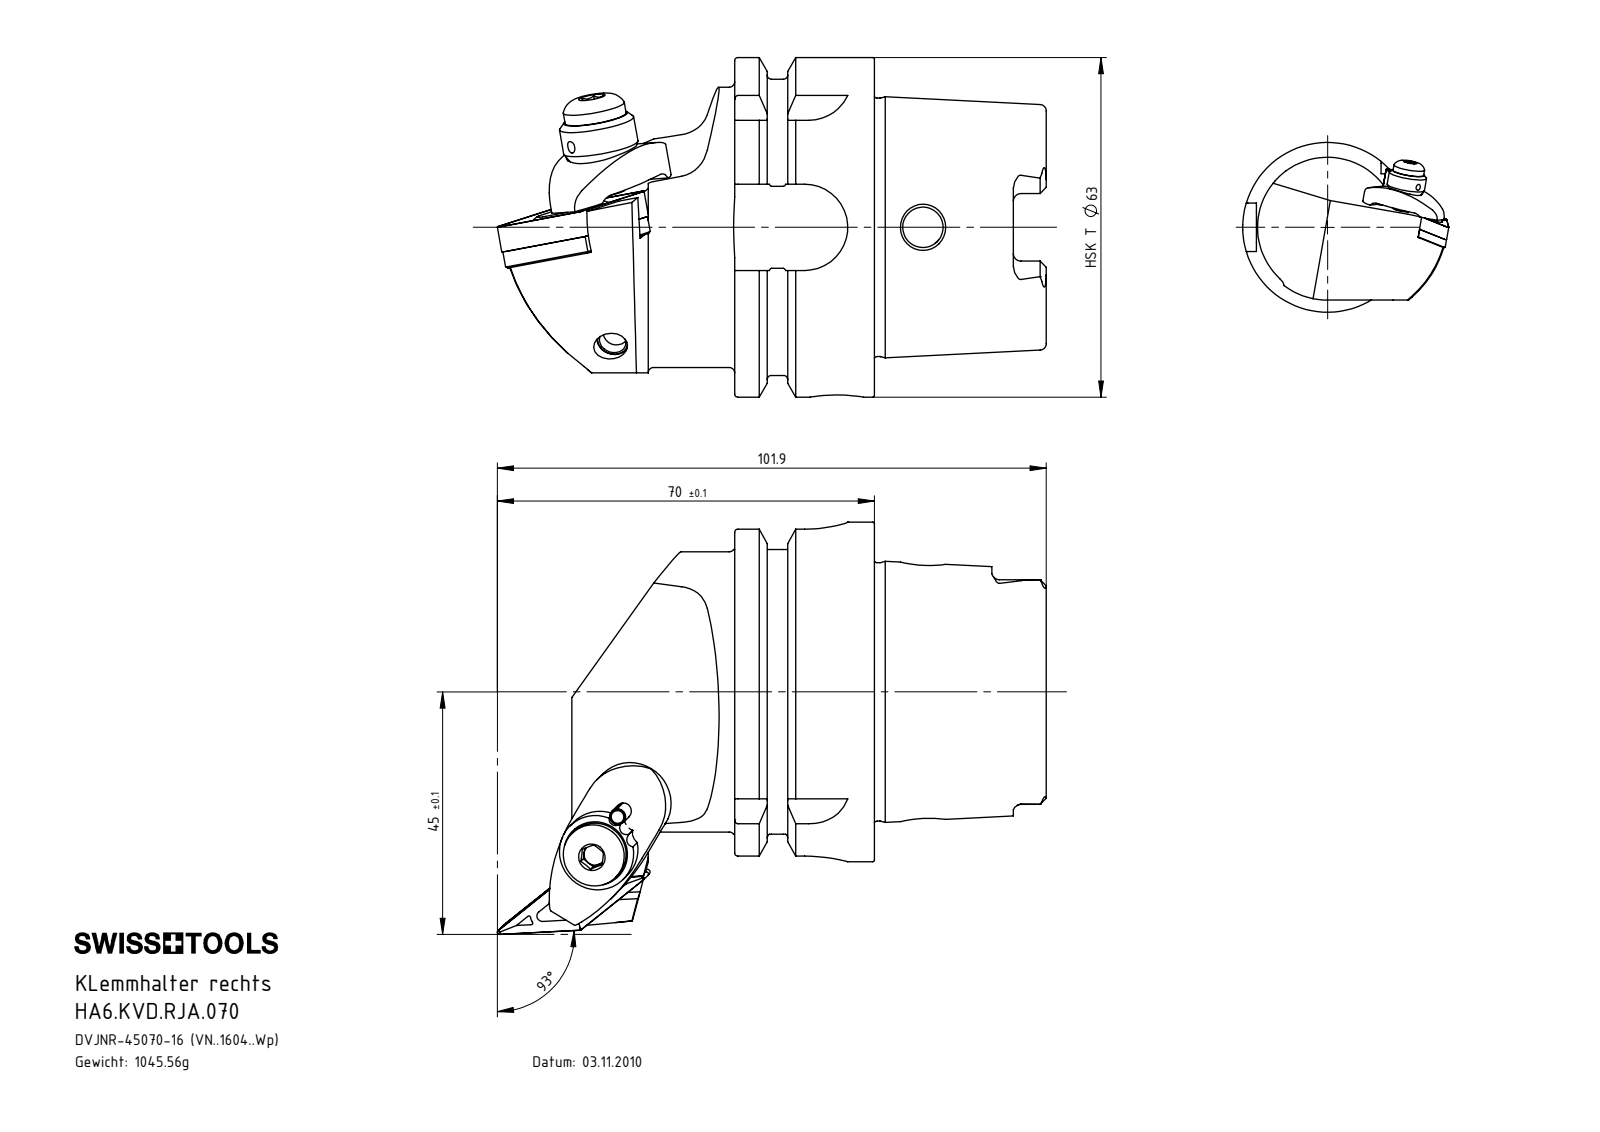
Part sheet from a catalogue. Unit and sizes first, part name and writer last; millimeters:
Units: millimetres
Overall size (bounding box): 101.9 × 76.5 × 63
Round holes (diameter × count): ⌀2 ×3, ⌀5 ×3, ⌀7 ×2, ⌀2.4 ×1, ⌀3 ×1, ⌀3.3 ×1, ⌀3.8 ×1, ⌀4.95 ×1, ⌀6 ×1, ⌀6.2 ×1, ⌀6.9 ×1, ⌀7.5 ×1
Round bosses / shafts (diameter × count): ⌀6 ×2, ⌀4 ×2, ⌀3 ×2, ⌀63 ×1, ⌀54.95 ×1, ⌀52 ×1, ⌀47.94 ×1, ⌀14 ×1
Partial cylindrical surfaces — rounded edges, fillets, slot ends (radius × count): R0.34 ×6, R0.59 ×6, R1.4 ×6, R0.4 ×4, R8 ×4, R1.5 ×3, R0.5 ×2, R2 ×2
Main face-to-face distances: 25.95, 16, 9.95, 31.9, 41.85, 57.85, 52.8, 21.8, 4.47, 11.85
Hole centre spacings: 7.94, 8.2, 14.3, 22.24, 7.95, 14.04
Volume: 129 784 mm³ · Surface area: 34 444 mm²
Bodies: 11 solids, 470 faces (129 planar, 150 cylindrical, 191 other)
Part name (STEP PRODUCT): WCC-ER5.102.005_A; WCC-ER5.102.012_B; VNMG160404; ISO 13337 - 3 x 12_PreviewCfg (+7 more)
STEP written by: SolidWorks 2017 (AUTOMOTIVE_DESIGN)
